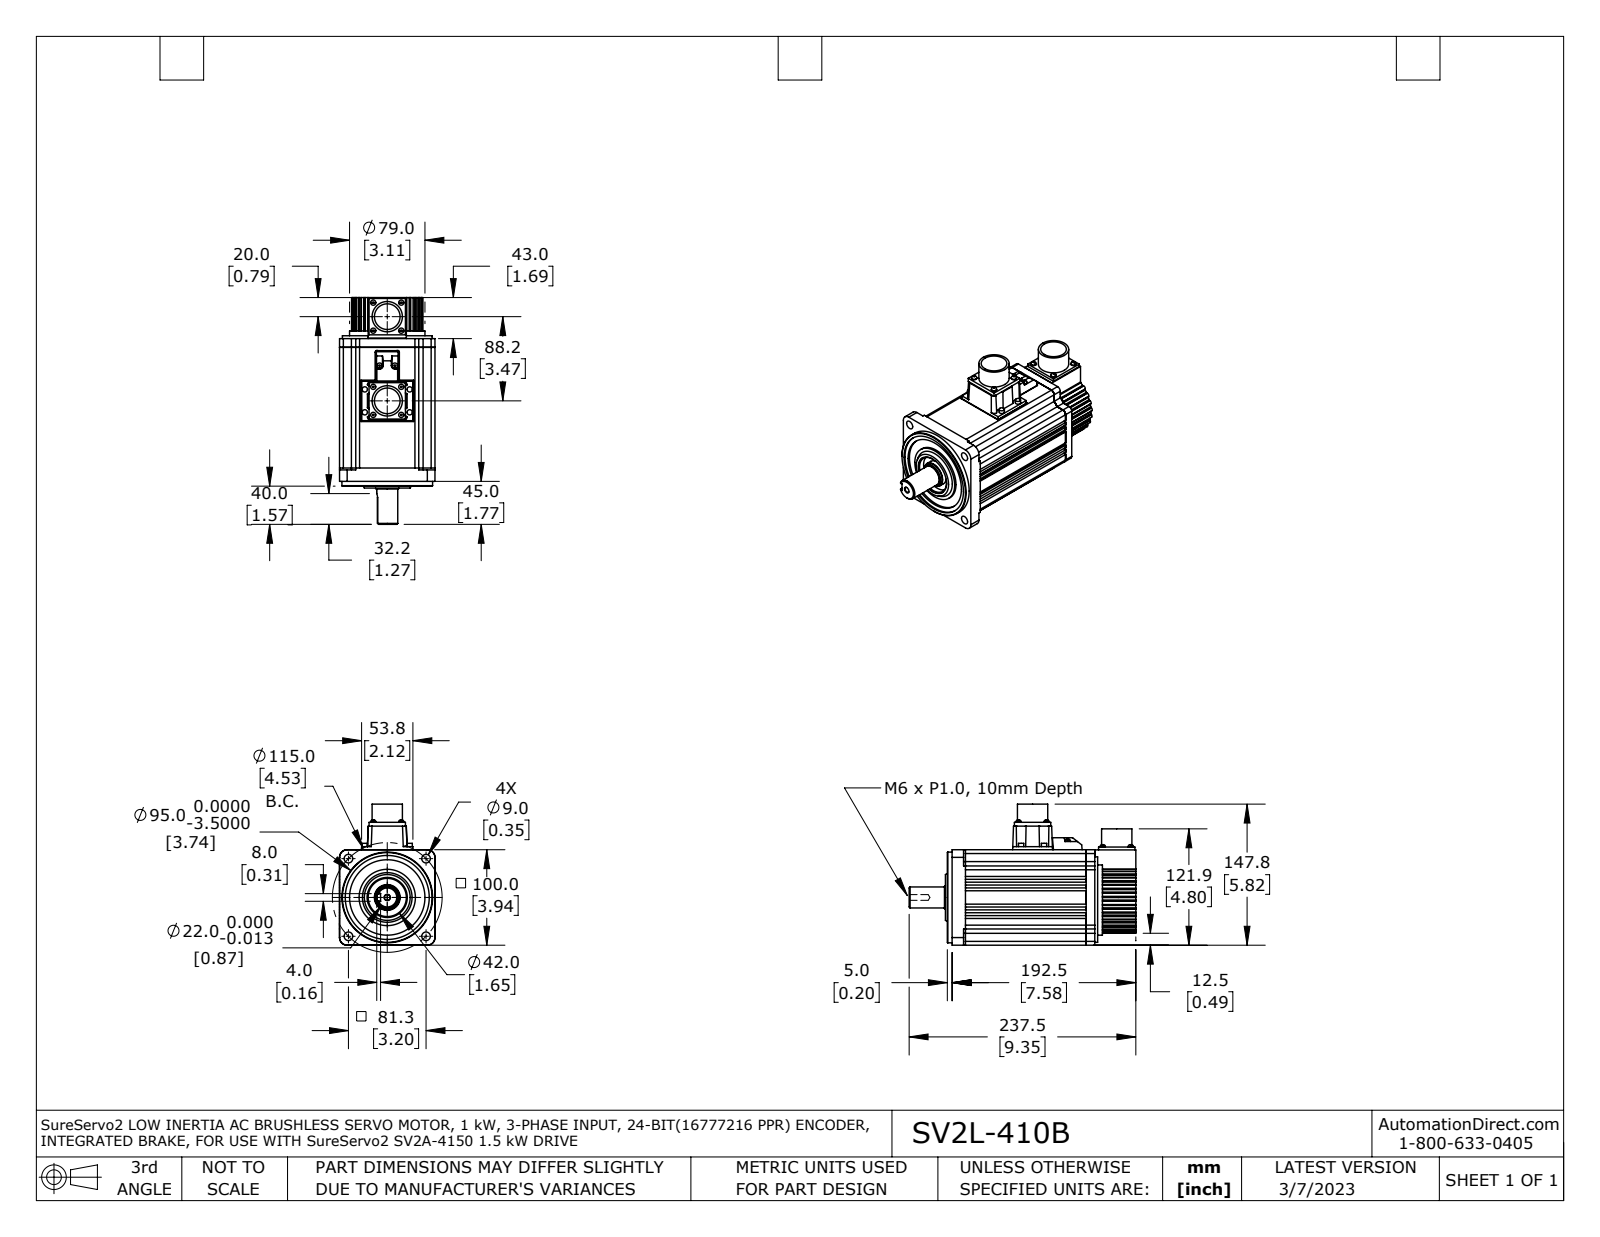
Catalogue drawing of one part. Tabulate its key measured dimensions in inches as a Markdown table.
| quantity | value |
| --- | --- |
| part name | SV2L-x10B coord fxt |
| STEP written by | SolidWorks 2021 (AUTOMOTIVE_DESIGN) |
| units | inches |
| bodies | 2 solids, 612 faces (269 planar, 269 cylindrical, 74 other) |
| overall size | 9.35 × 5.817 × 3.937 |
| volume | 99.63 in³ |
| surface area | 203.3 in² |
| round holes (diameter × count) | 0.354 × 4, 0.118 × 2, 0.13 × 2, 1.058 × 2, 0.236 × 1, 0.984 × 1, 1.024 × 1, 1.575 × 1, 1.654 × 1, 3.11 × 1, 3.465 × 1 |
| round bosses / shafts (diameter × count) | 0.217 × 8, 0.213 × 6, 1.25 × 2, 3.74 × 1, 3.701 × 1, 3.11 × 1, 2.323 × 1, 1.063 × 1 |
| partial cylindrical surfaces (radius × count) | 0.039 × 44, 0.079 × 21, 0.157 × 21, 0.008 × 8, 0.079 × 2, 1.397 × 1, 1.88 × 1, 1.949 × 1 |
| main face-to-face distances | 0.669, 0.118, 3.937, 3.268, 0.236, 2.598, 0.433, 1.575, 1.378, 1.102 |
| hole center spacings | 2.264, 3.202, 1.488, 2.042, 4.528, 0.63, 3.472 |
